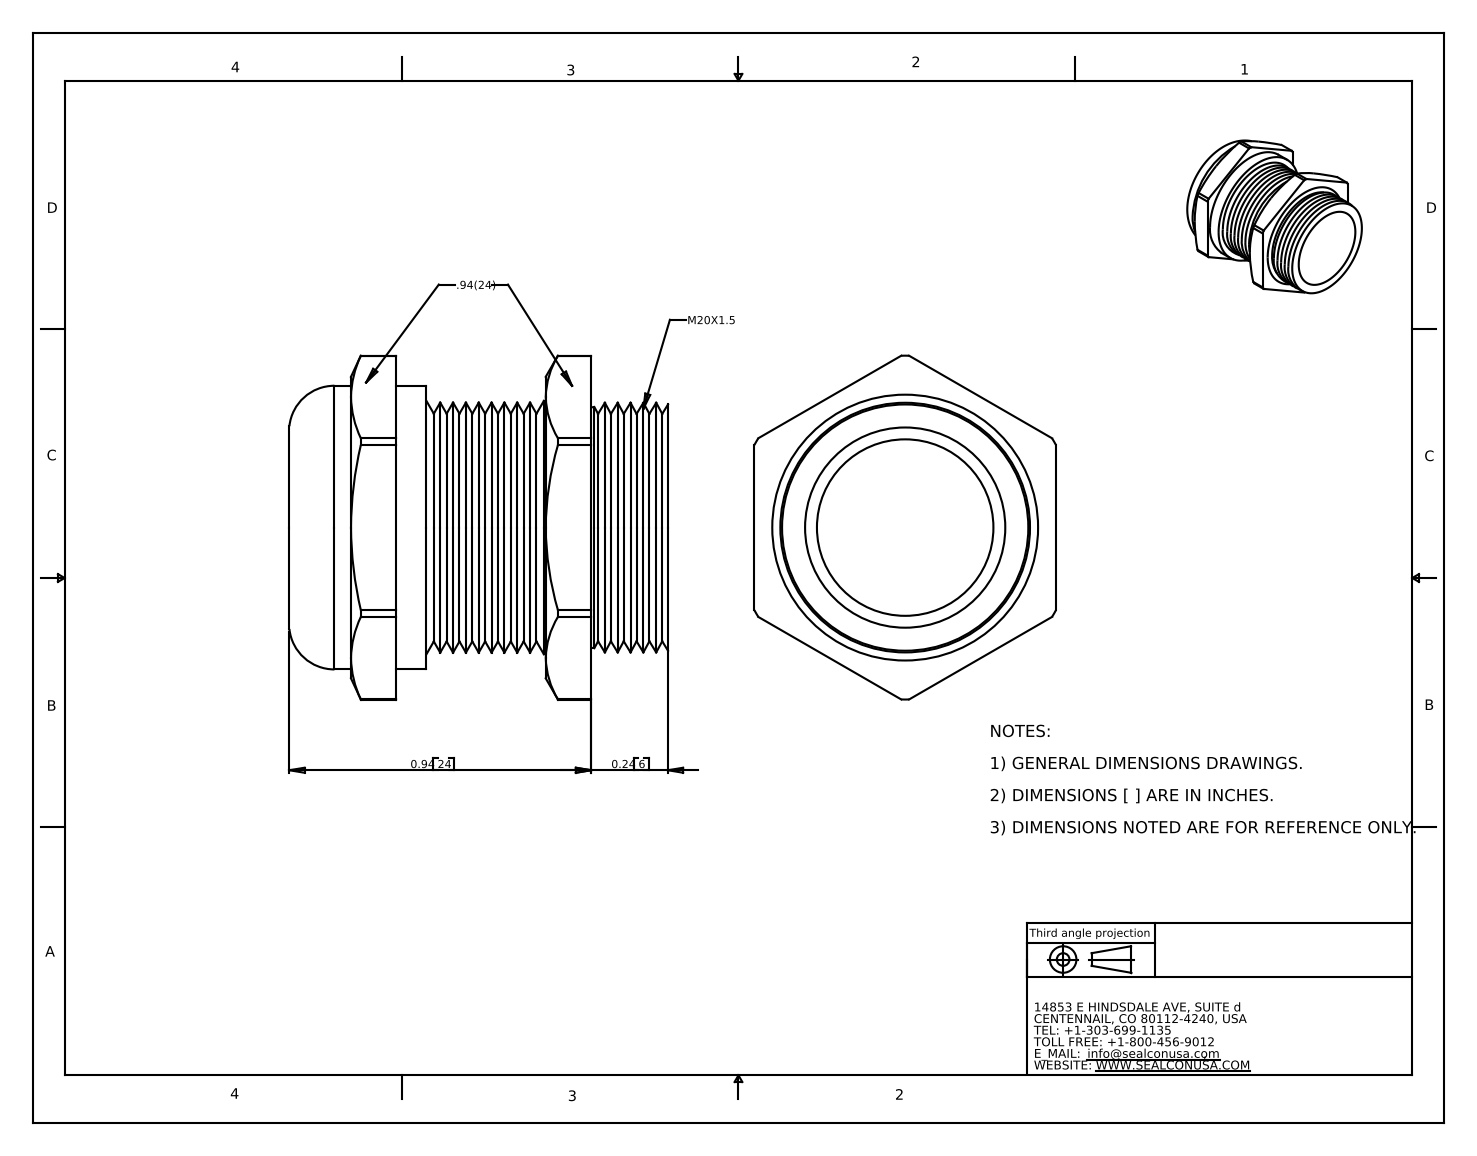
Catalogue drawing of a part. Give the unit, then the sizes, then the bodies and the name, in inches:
Units: inches
Overall size (bounding box): 1.18 × 1.072 × 0.94
Round holes (diameter × count): ⌀0.55 ×1, ⌀0.632 ×1
Round bosses / shafts (diameter × count): ⌀0.884 ×1, ⌀0.79 ×1
Partial cylindrical surfaces — rounded edges, fillets, slot ends (radius × count): R0.536 ×1
Main face-to-face distances: 0.94, 0.141, 0.607, 0.748, 0.988, 0.381, 0.24, 0.466, 0.847, 0.235
Volume: 0.335 in³ · Surface area: 8.885 in²
Bodies: 2 solids, 129 faces (21 planar, 26 cylindrical, 82 other)
Part name (STEP PRODUCT): CD22MA-BR
STEP written by: SolidWorks 2007 (CONFIG_CONTROL_DESIGN)
